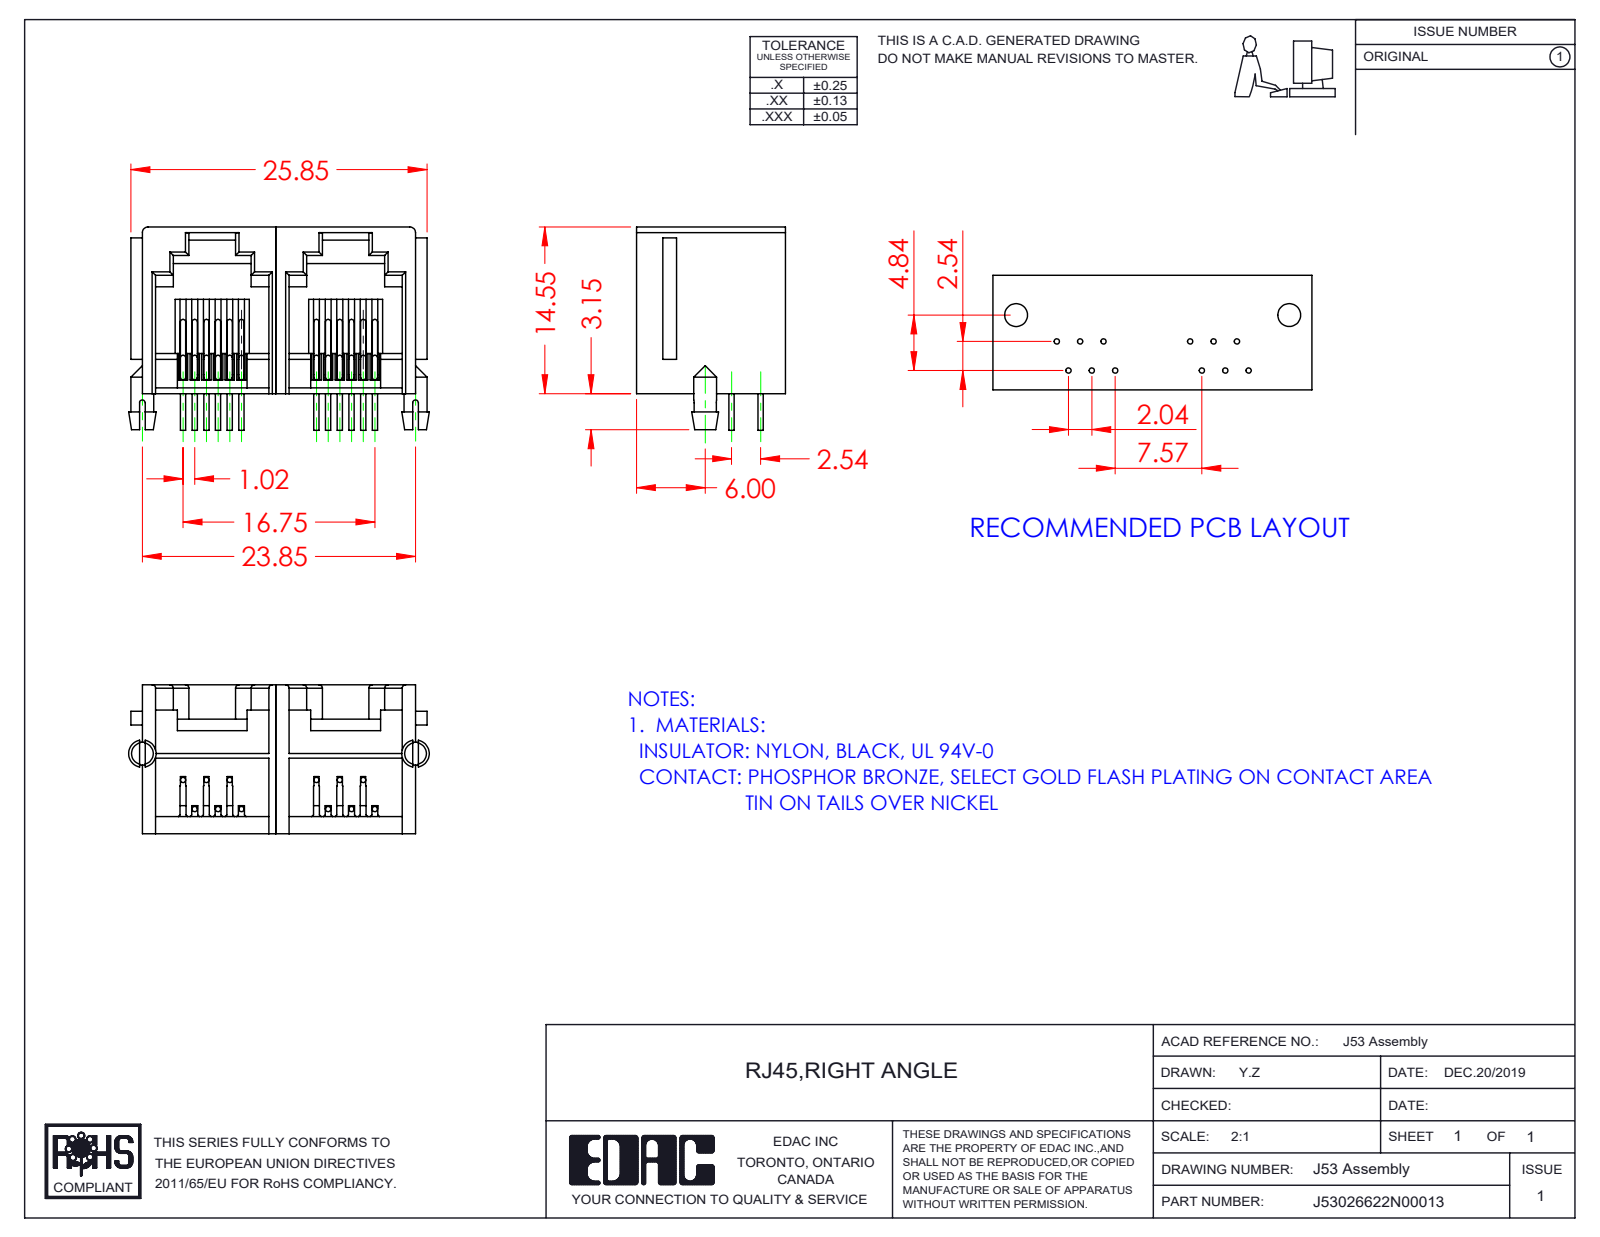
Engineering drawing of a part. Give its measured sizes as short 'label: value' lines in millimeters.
name: 53 Contact - 4; 53 Contact - 3; 53 Contacts; RJ53026622N00013 (+6 more)
written by: SolidWorks 2016 (CONFIG_CONTROL_DESIGN)
unit: mm
bodies: 14 solids, 595 faces (410 planar, 128 cylindrical, 57 other)
size: 26.25 × 17.75 × 13
volume: 1 800 mm³; area: 4 280 mm²
bosses: 36× ⌀0.46, 2× ⌀2
rounds: 14× R0.3, 10× R0.5, 2× R0.25, 1× R0.67
face distances: 11.65, 1.16, 11.04, 12.2, 22.69, 10.49, 12.81, 0.61, 9.88, 3
